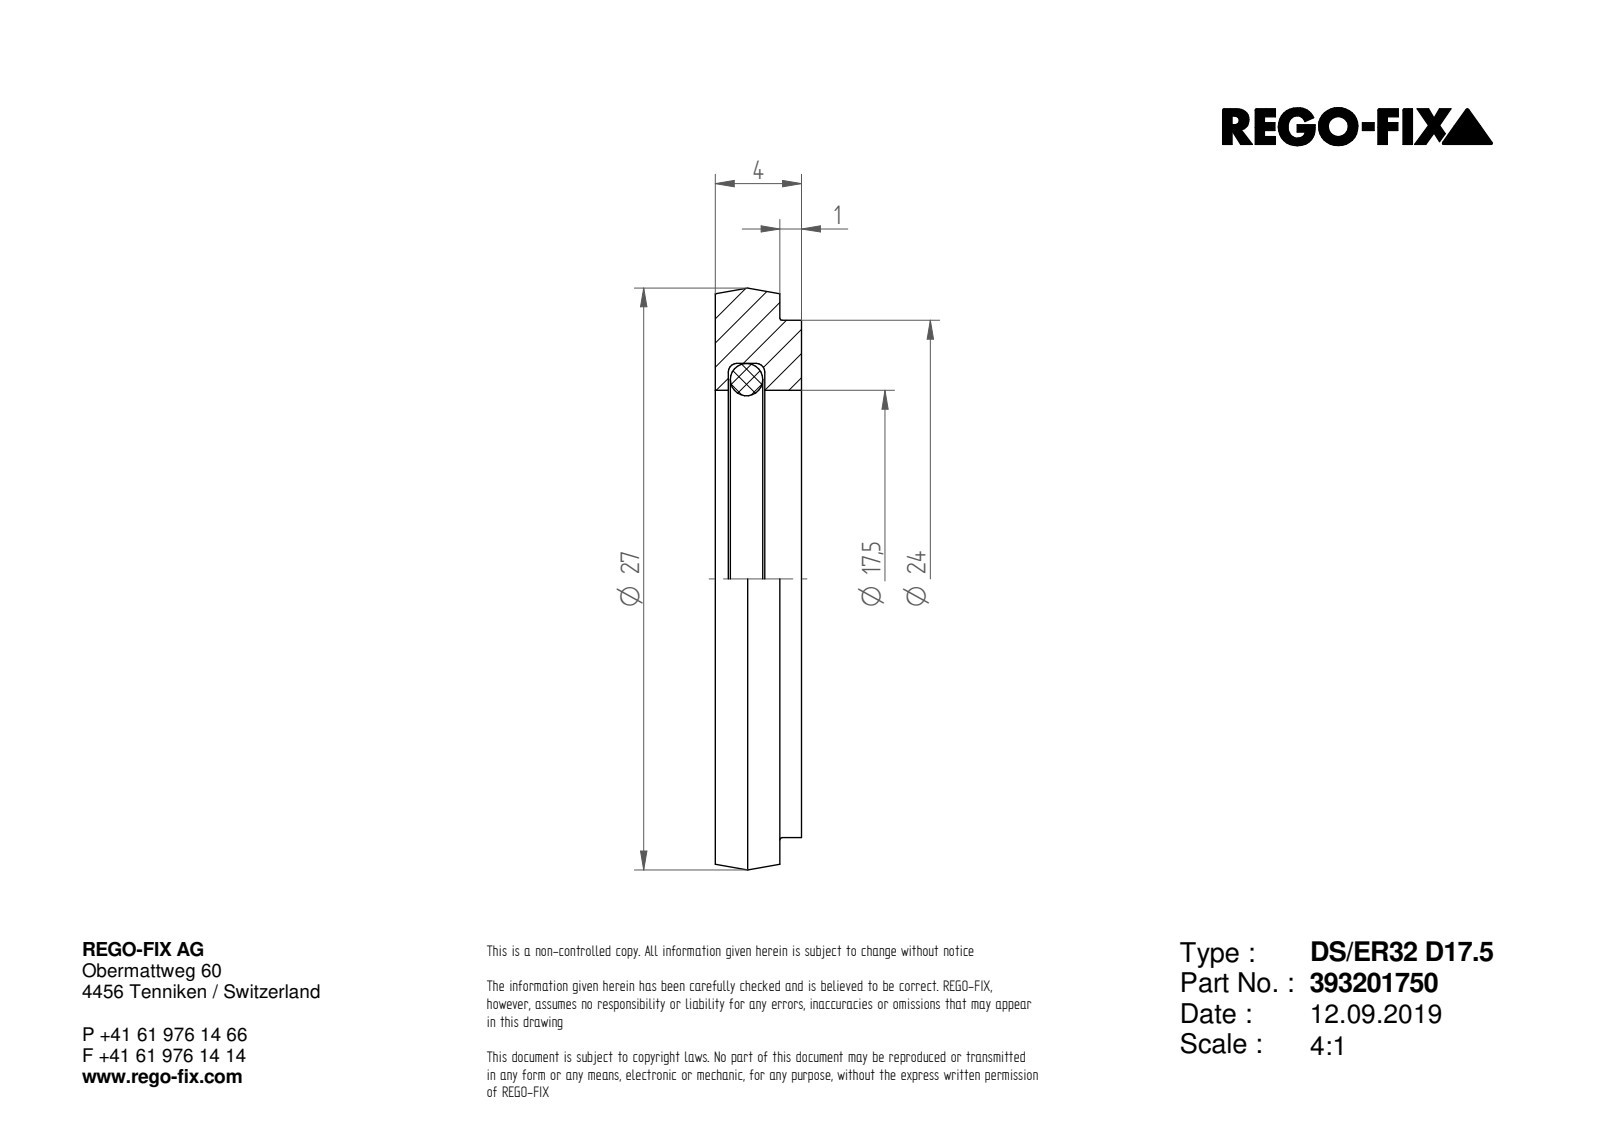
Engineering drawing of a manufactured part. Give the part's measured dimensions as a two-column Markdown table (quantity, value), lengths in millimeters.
| quantity | value |
| --- | --- |
| part name | NOCUT |
| STEP written by | SIEMENS PLM Software Solid Edge ST10 (AUTOMOTIVE_DESIGN) |
| units | millimeters |
| bodies | 1 solid, 7 faces (3 planar, 3 cylindrical, 1 other) |
| overall size | 27 × 27 × 4 |
| volume | 1 208 mm³ |
| surface area | 1 211 mm² |
| round holes (diameter × count) | 17.5 × 1 |
| round bosses / shafts (diameter × count) | 27 × 1, 24 × 1 |
| main face-to-face distances | 4, 1, 3 |
